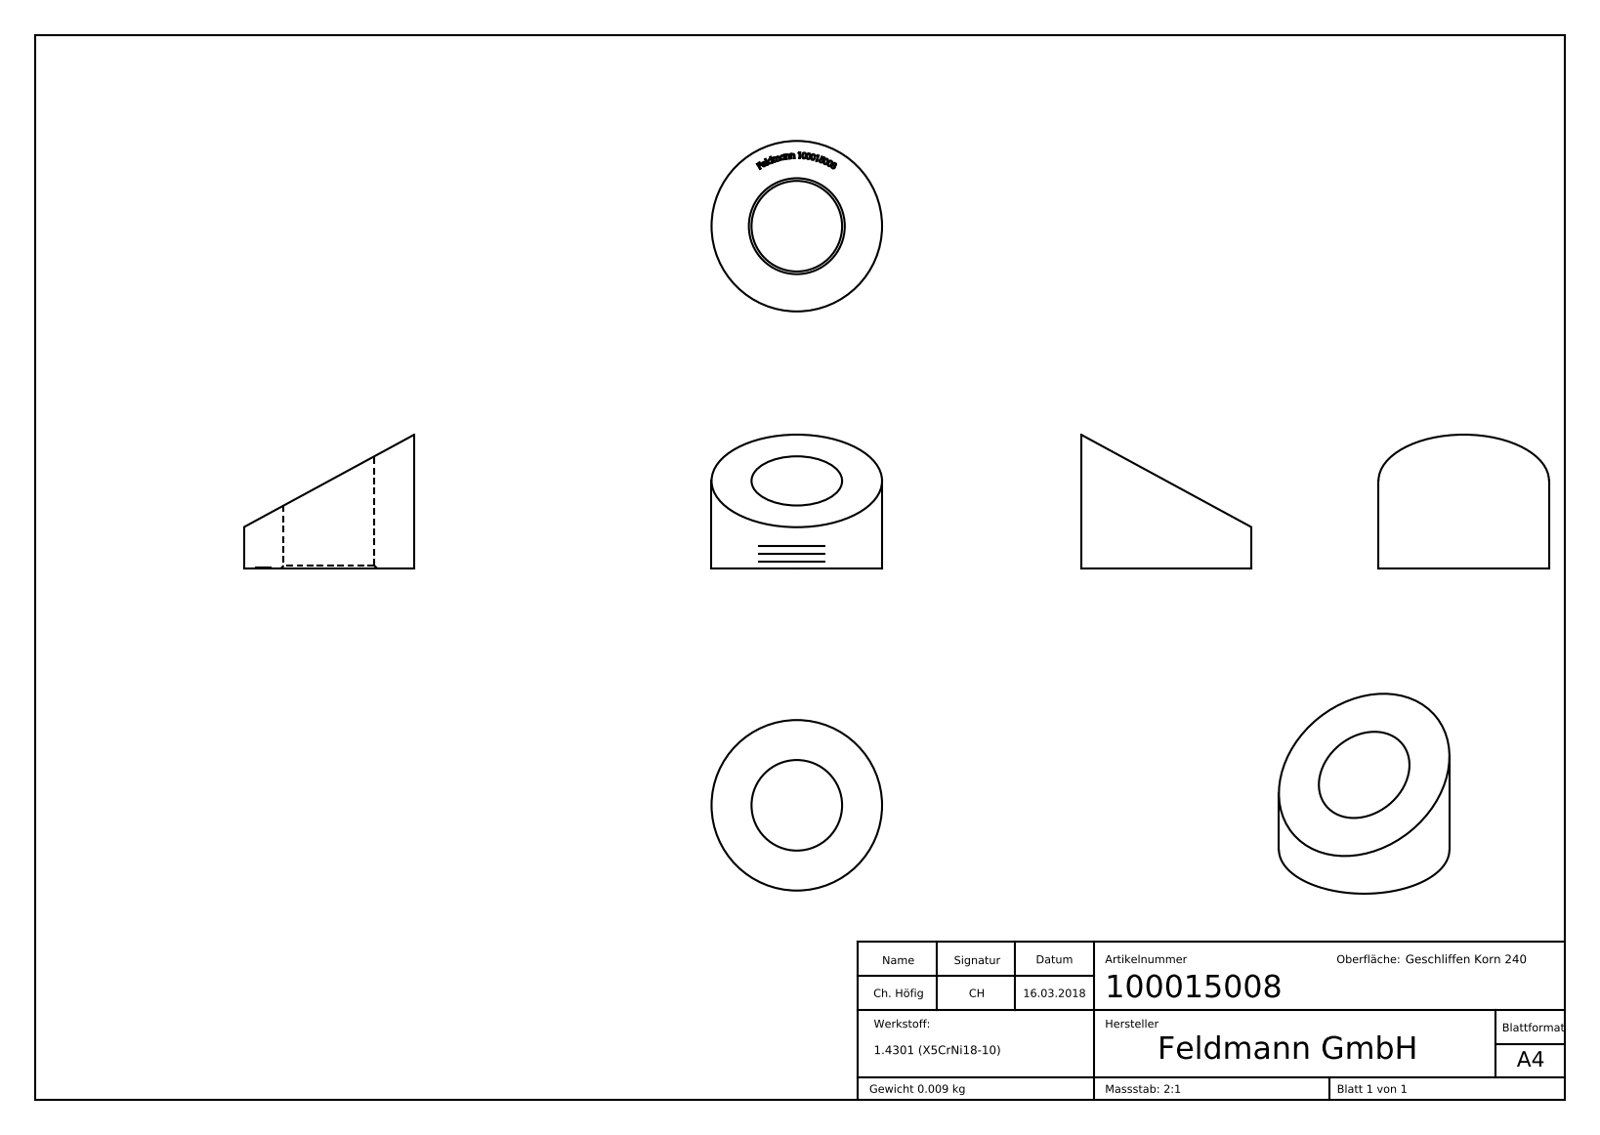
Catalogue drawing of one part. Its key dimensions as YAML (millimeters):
part_name: "100015008"
step_written_by: "SolidWorks 2015 (CONFIG_CONTROL_DESIGN)"
units: millimeters
bodies: {solids: 1, faces: 225, planar: 101, cylindrical: 4, other: 120}
overall_size: [16, 16, 12.54]
volume: 1182
surface_area: 940
round_holes:
  - {diameter: 8.5, count: 1}
round_bosses_or_shafts:
  - {diameter: 16, count: 1}
face_to_face_distances: [0.34, 0.53, 0.39, 0.58, 0.48, 0.32, 0.31, 0.54, 0.47, 0.52]
